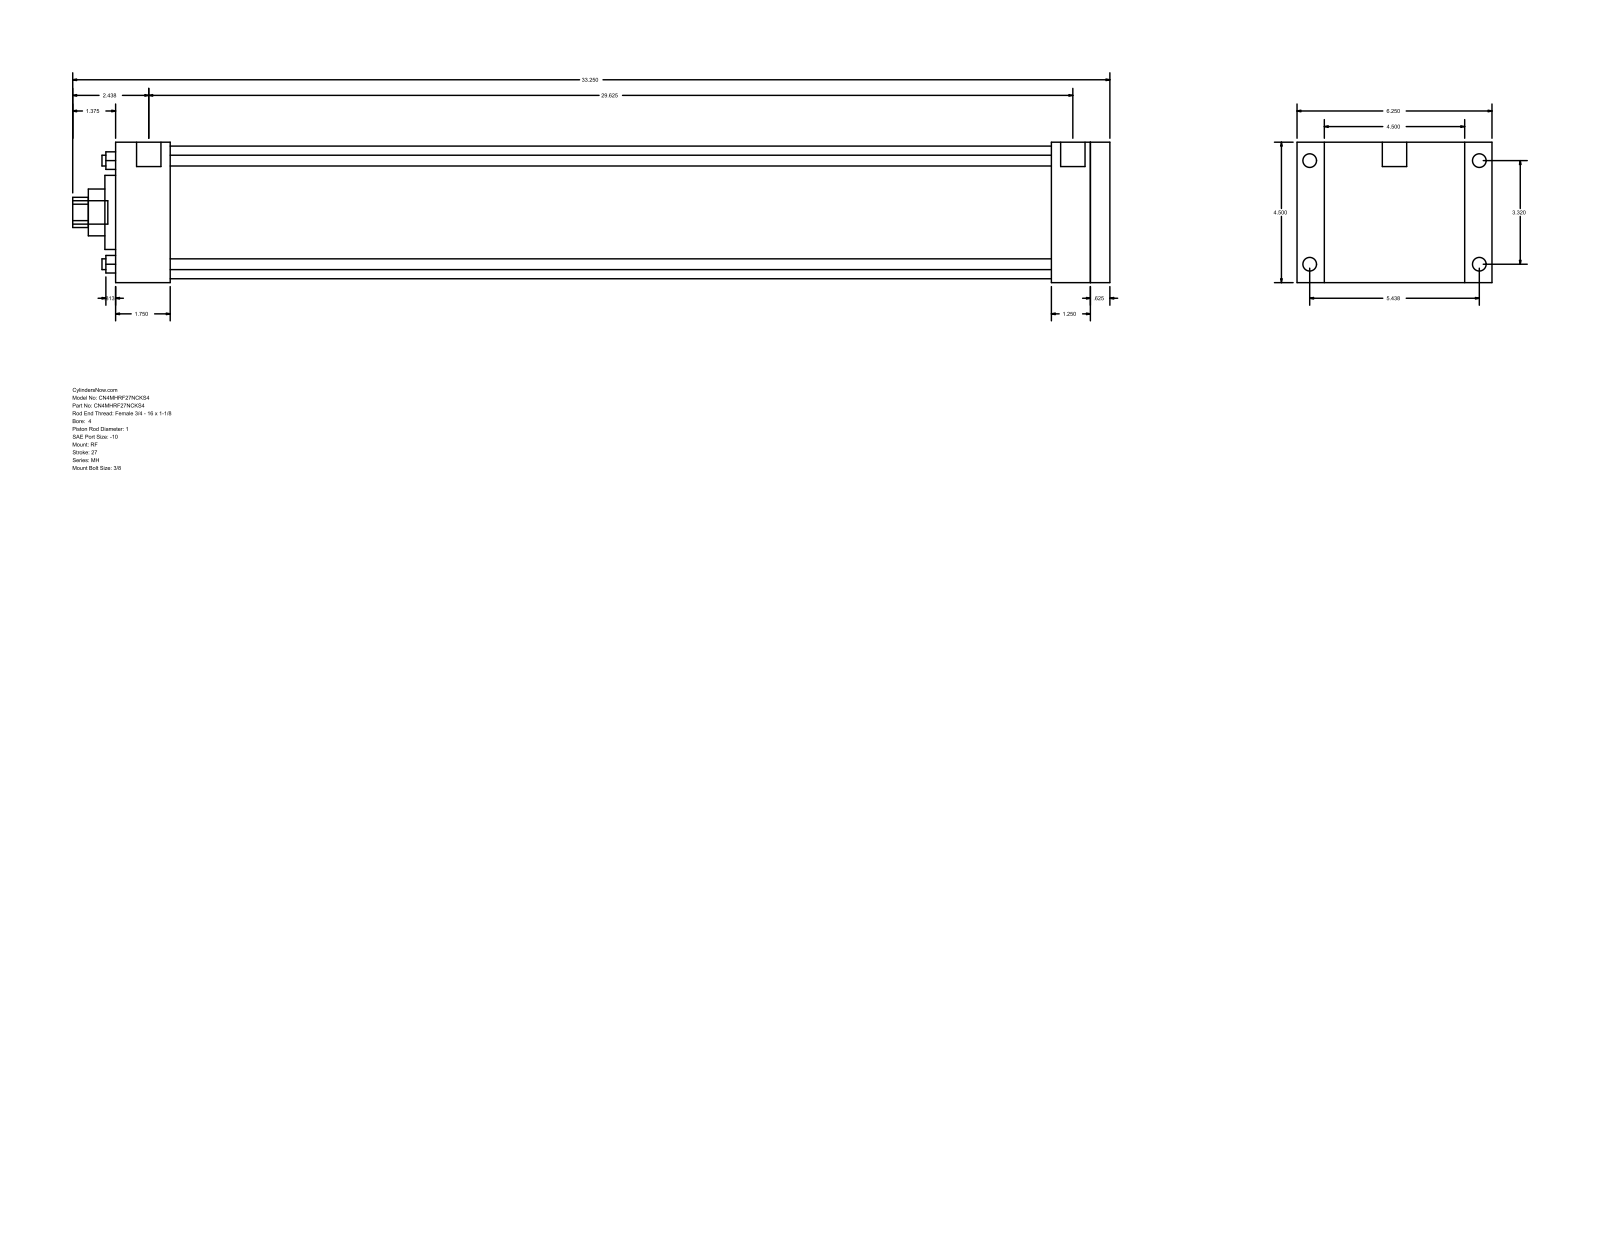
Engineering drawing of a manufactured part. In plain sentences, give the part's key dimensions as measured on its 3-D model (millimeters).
The part is named "MH_RF__0400_1". Its 3-D file was written by "GSSL Pune (CONFIG_CONTROL_DESIGN)". It is 0 solids with 94 faces: 65 planar, 29 cylindrical and 0 other. Overall it measures 844.55 by 158.75 by 114.3 millimeters. Round holes: 4 of diameter 8.76, 1 of diameter 25.4, 1 of diameter 38.1, 1 of diameter 60.33, 1 of diameter 107.95. Round bosses or shafts: 4 of diameter 11.13, 4 of diameter 8.73, 2 of diameter 19.84, 1 of diameter 19.05. Partial cylindrical surfaces (rounded edges, fillets, slot ends): 1 of radius 12.29. The main face-to-face distances are 114.3, 809.63, 793.75, 15.88, 47.63, 44.46, 749.29, 765.17, 762, 717.54. The hole center spacings are 59.62, 84.32, 119.25.
